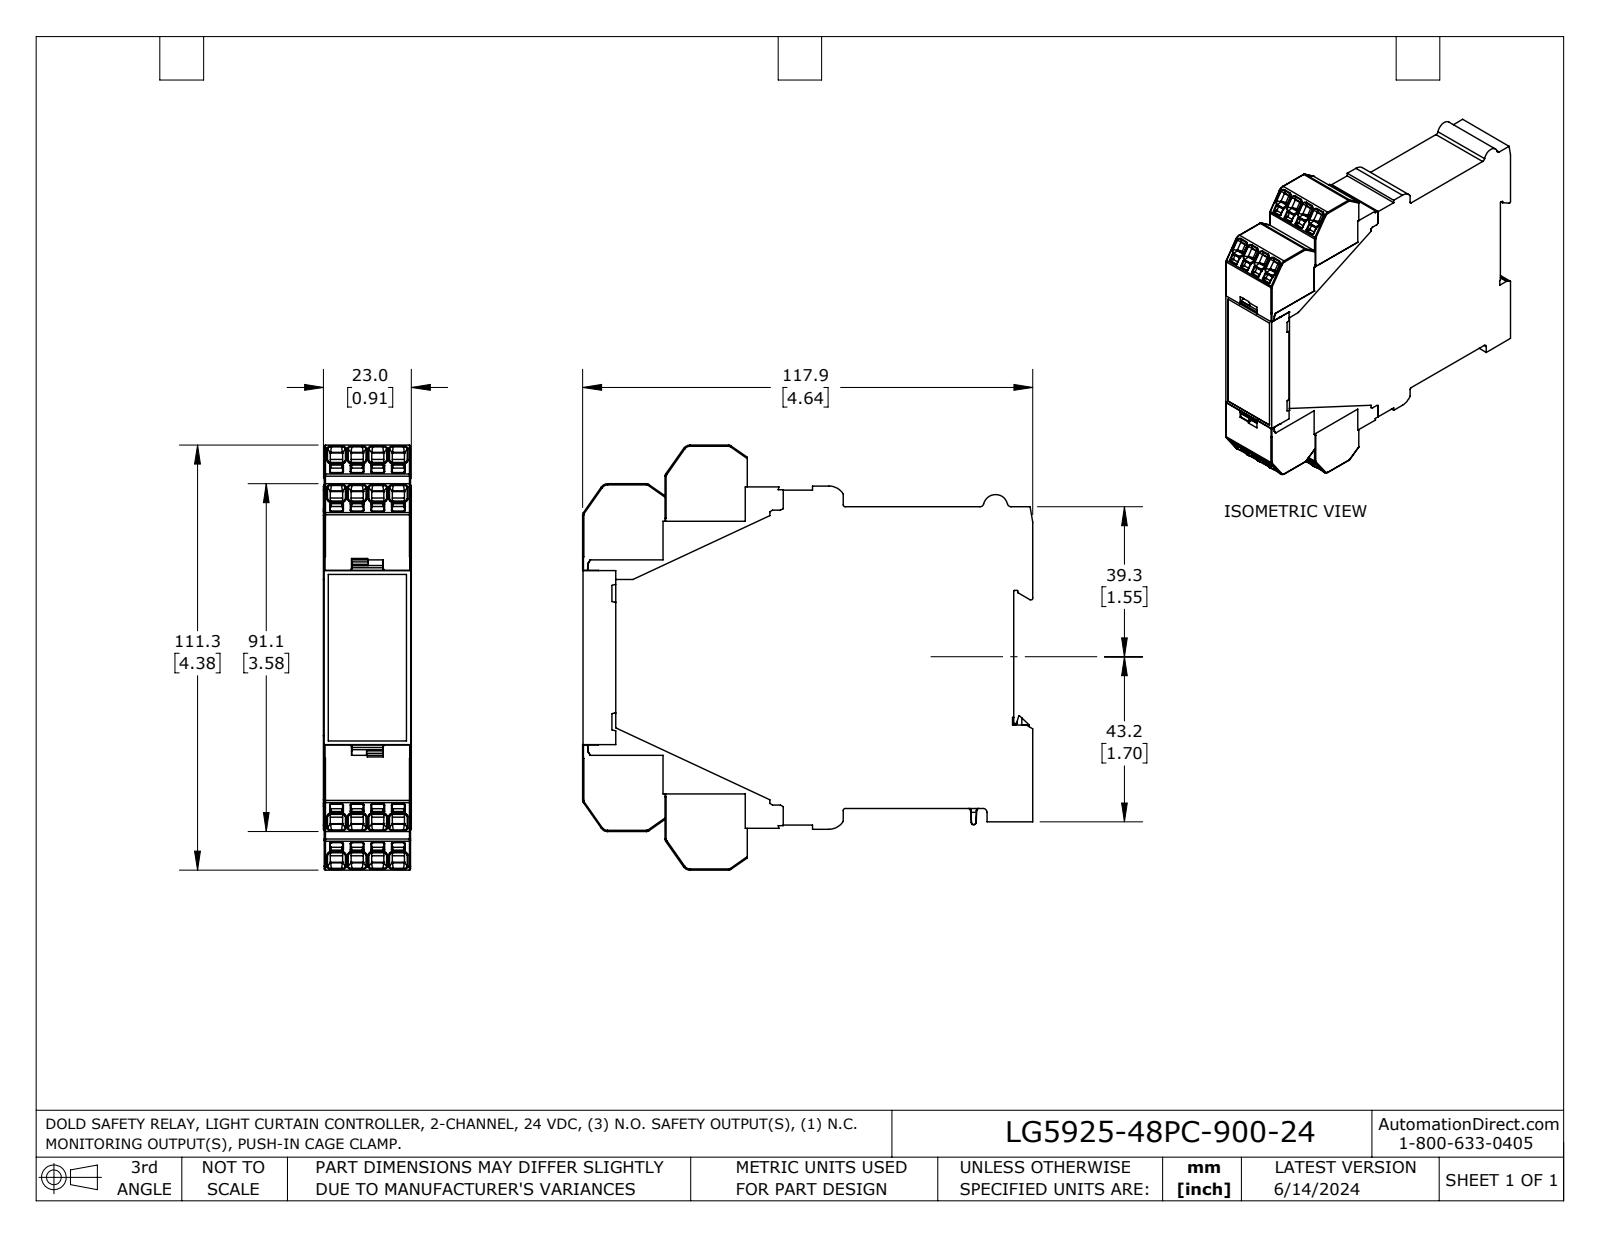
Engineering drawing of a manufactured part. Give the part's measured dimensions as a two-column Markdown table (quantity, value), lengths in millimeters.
| quantity | value |
| --- | --- |
| part name | LG5925 |
| STEP written by | SolidWorks 2023 (AUTOMOTIVE_DESIGN) |
| units | millimeters |
| bodies | 18 solids, 1620 faces (1027 planar, 335 cylindrical, 258 other) |
| overall size | 118 × 111.3 × 23 |
| volume | 244 700 mm³ |
| surface area | 49 390 mm² |
| round holes (diameter × count) | 1.7 × 4, 1.2 × 1 |
| round bosses / shafts (diameter × count) | 1.3 × 1 |
| partial cylindrical surfaces (radius × count) | 0.2 × 127, 0.2 × 32, 0.3 × 28, 1 × 16, 0.1 × 10, 0.5 × 7, 0.1 × 6, 0.1 × 4 |
| main face-to-face distances | 23, 22.8, 10.1, 22.9, 22.7, 21.5, 61.3, 75.2, 3.8, 13.9 |
| hole center spacings | 16.2, 21.5, 26.9 |
